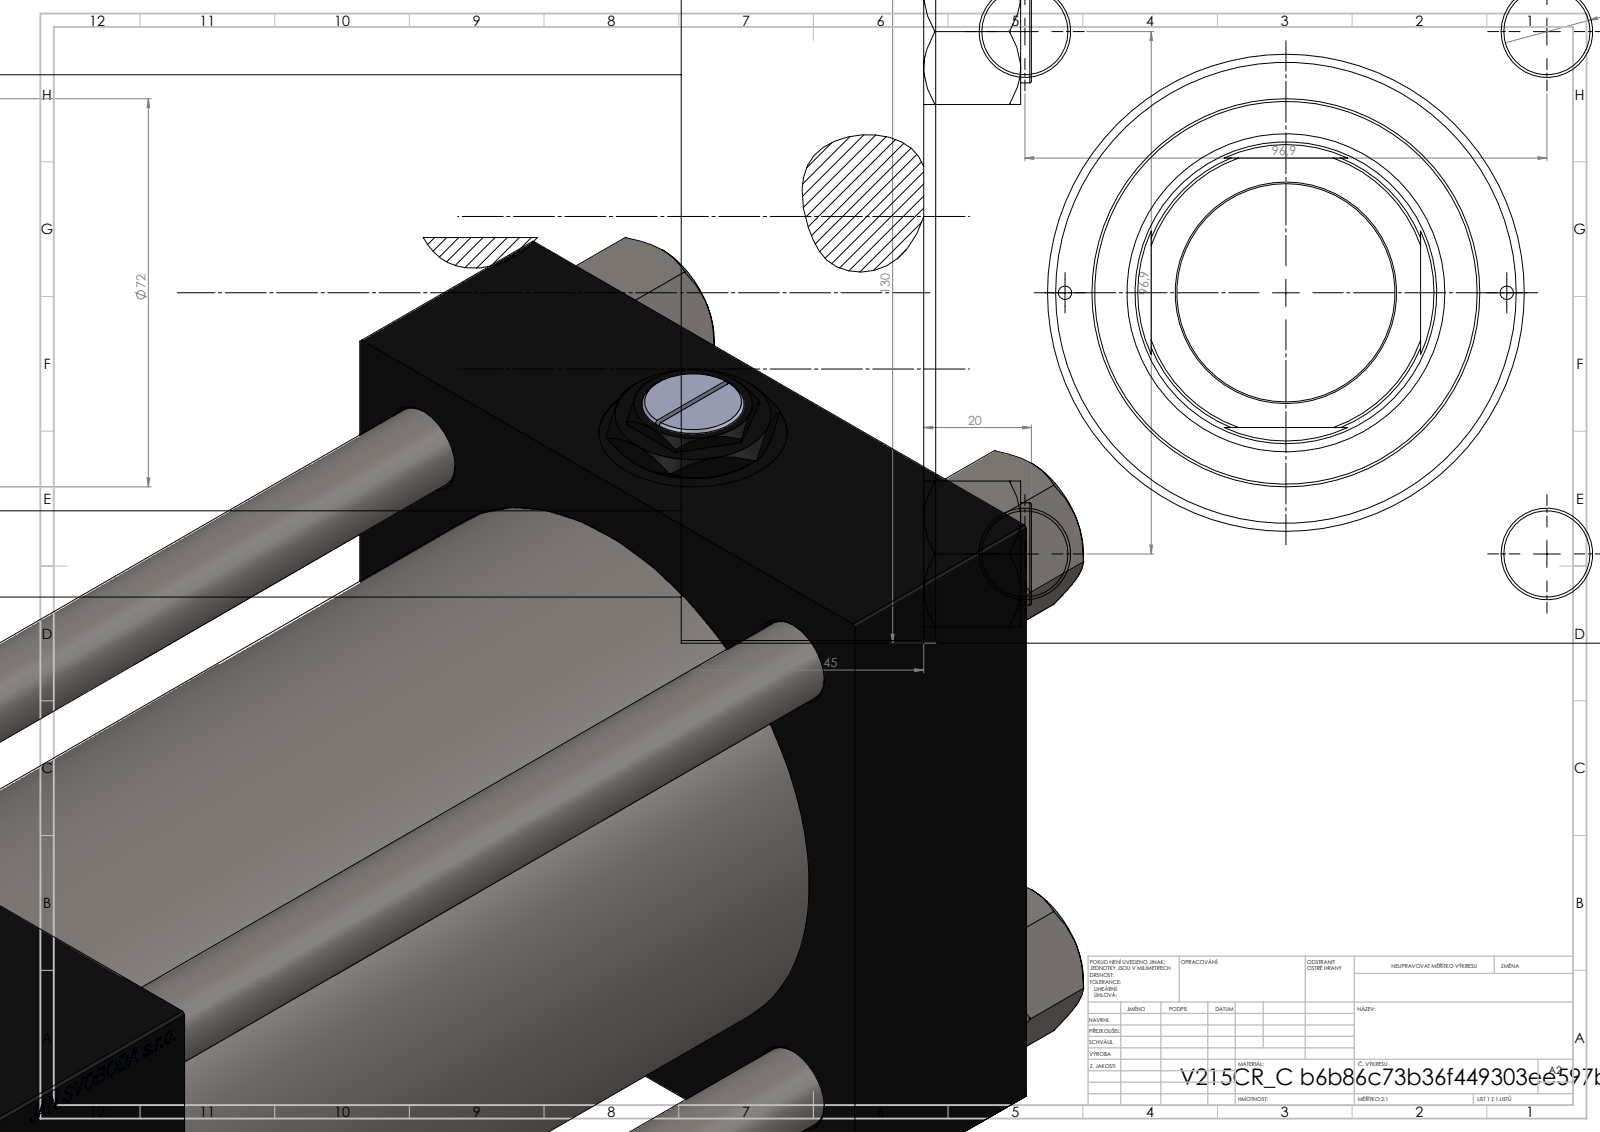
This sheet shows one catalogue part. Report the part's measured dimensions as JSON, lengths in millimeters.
{"part_name": "V215CR_VCP_C; Zatka_pro_OIL_PORT; NUT_M5_C; V215_VC_A (+2 more)", "step_written_by": "SolidWorks 2019 (CONFIG_CONTROL_DESIGN)", "units": "millimeters", "bodies": {"solids": 13, "faces": 1303, "planar": 623, "cylindrical": 102, "other": 578}, "overall_size": [348, 137, 137], "volume_mm3": 2905000, "surface_area_mm2": 448200, "round_holes": [[16, 4], [2.5, 2], [7, 2], [26.44, 2], [35, 2], [40.5, 1], [56, 1], [59, 1], [76, 1], [85.5, 1], [100, 1]], "round_bosses_or_shafts": [[19, 4], [106, 1], [72, 1]], "partial_cylinders_radius": [[27, 1]], "face_to_face_distances": [130, 45, 293, 248, 72, 221, 176, 51, 197, 125], "hole_center_spacings": [49.02, 68.52, 96.9, 101.73, 41, 137.04, 82]}
